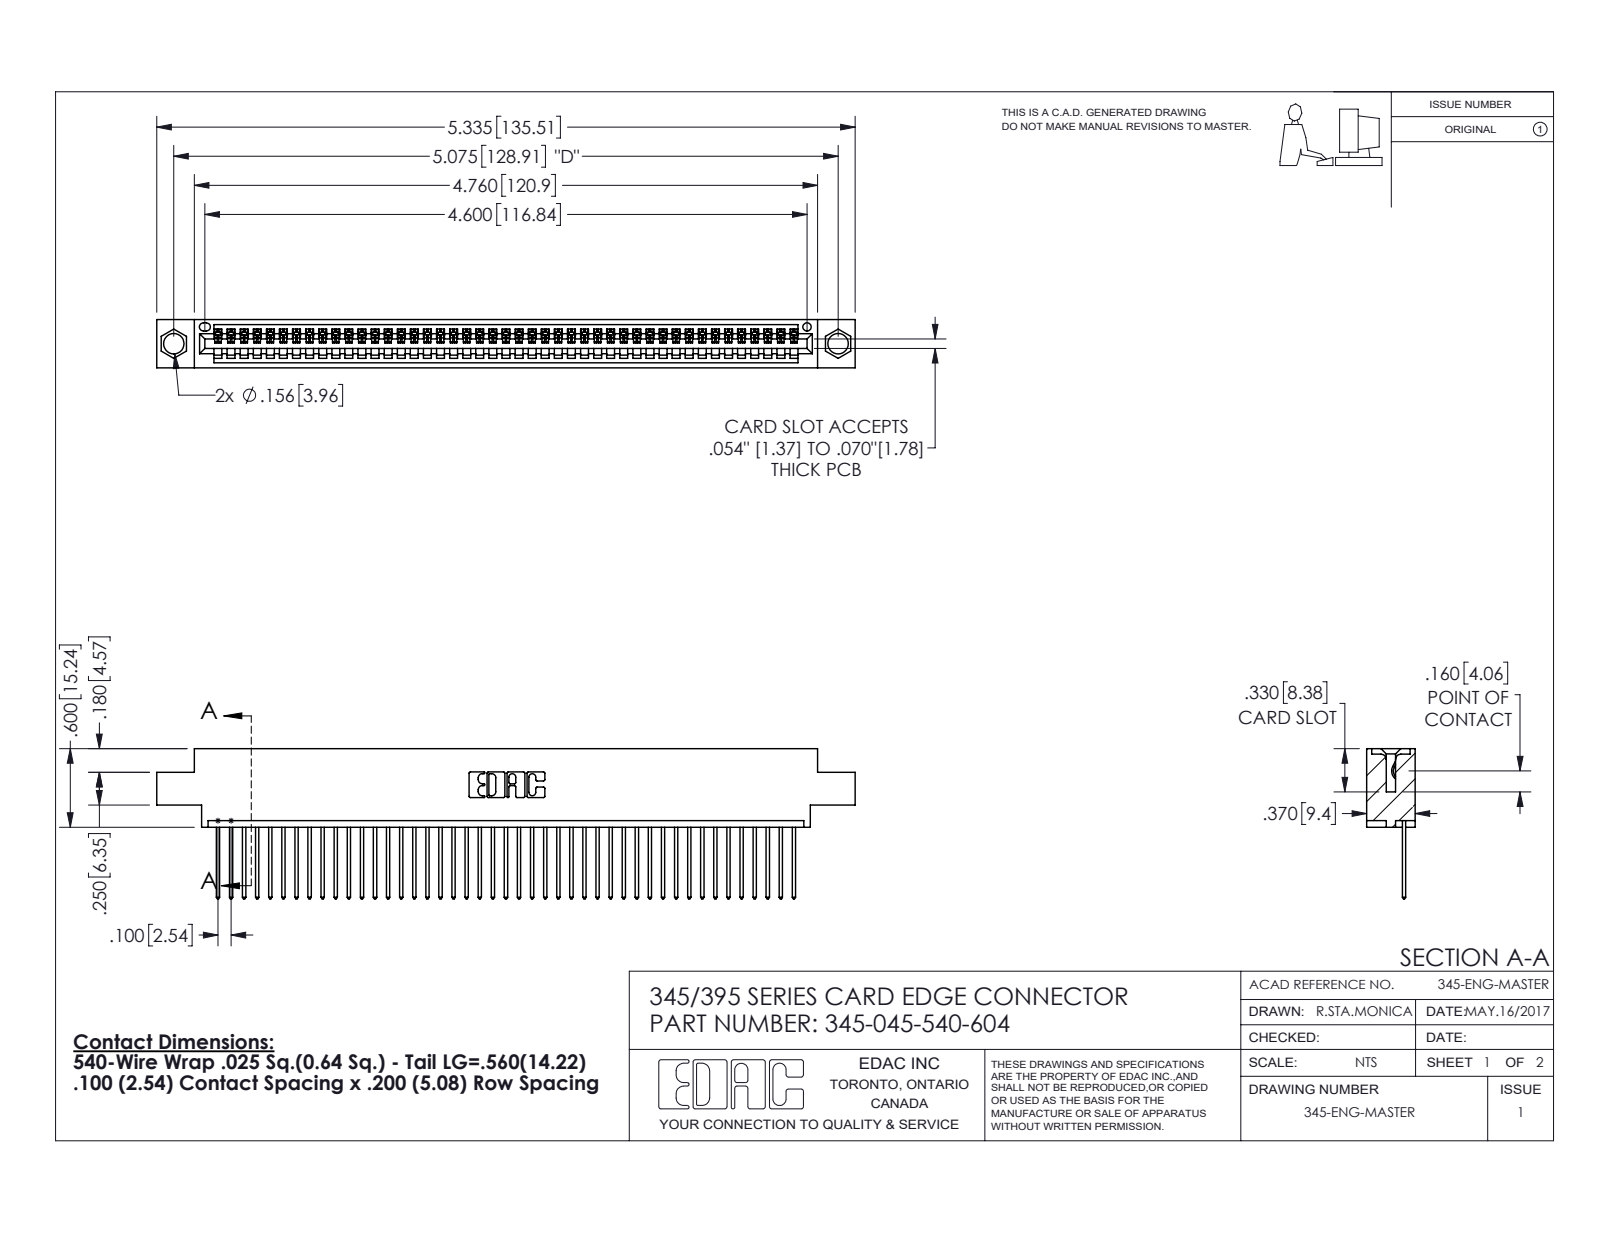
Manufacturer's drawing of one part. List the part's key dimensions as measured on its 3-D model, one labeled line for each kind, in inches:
Part name (STEP PRODUCT): 345-292-001_345-293-140; 345 Part_0.170 Offset - 0.156 Dia-TH; 345-045-540-604
STEP written by: SolidWorks 2016 (CONFIG_CONTROL_DESIGN)
Units: inches
Bodies: 46 solids, 2740 faces (1884 planar, 856 cylindrical, 0 other)
Overall size (bounding box): 5.335 × 1.147 × 0.37
Volume: 0.778 in³ · Surface area: 26.92 in²
Round holes (diameter × count): ⌀0.156 ×2, ⌀0.064 ×1
Partial cylindrical surfaces — rounded edges, fillets, slot ends (radius × count): R0.006 ×90, R0.01 ×90, R0.01 ×22, R0.007 ×6, R0.031 ×6, R0.026 ×3, R0.031 ×2, R0.04 ×2
Main face-to-face distances: 0.298, 0.072, 0.37, 0.098, 0.272, 0.025, 0.2, 0.225, 0.175, 0.149
Hole centre spacings: 0.27, 4.839, 5.075
